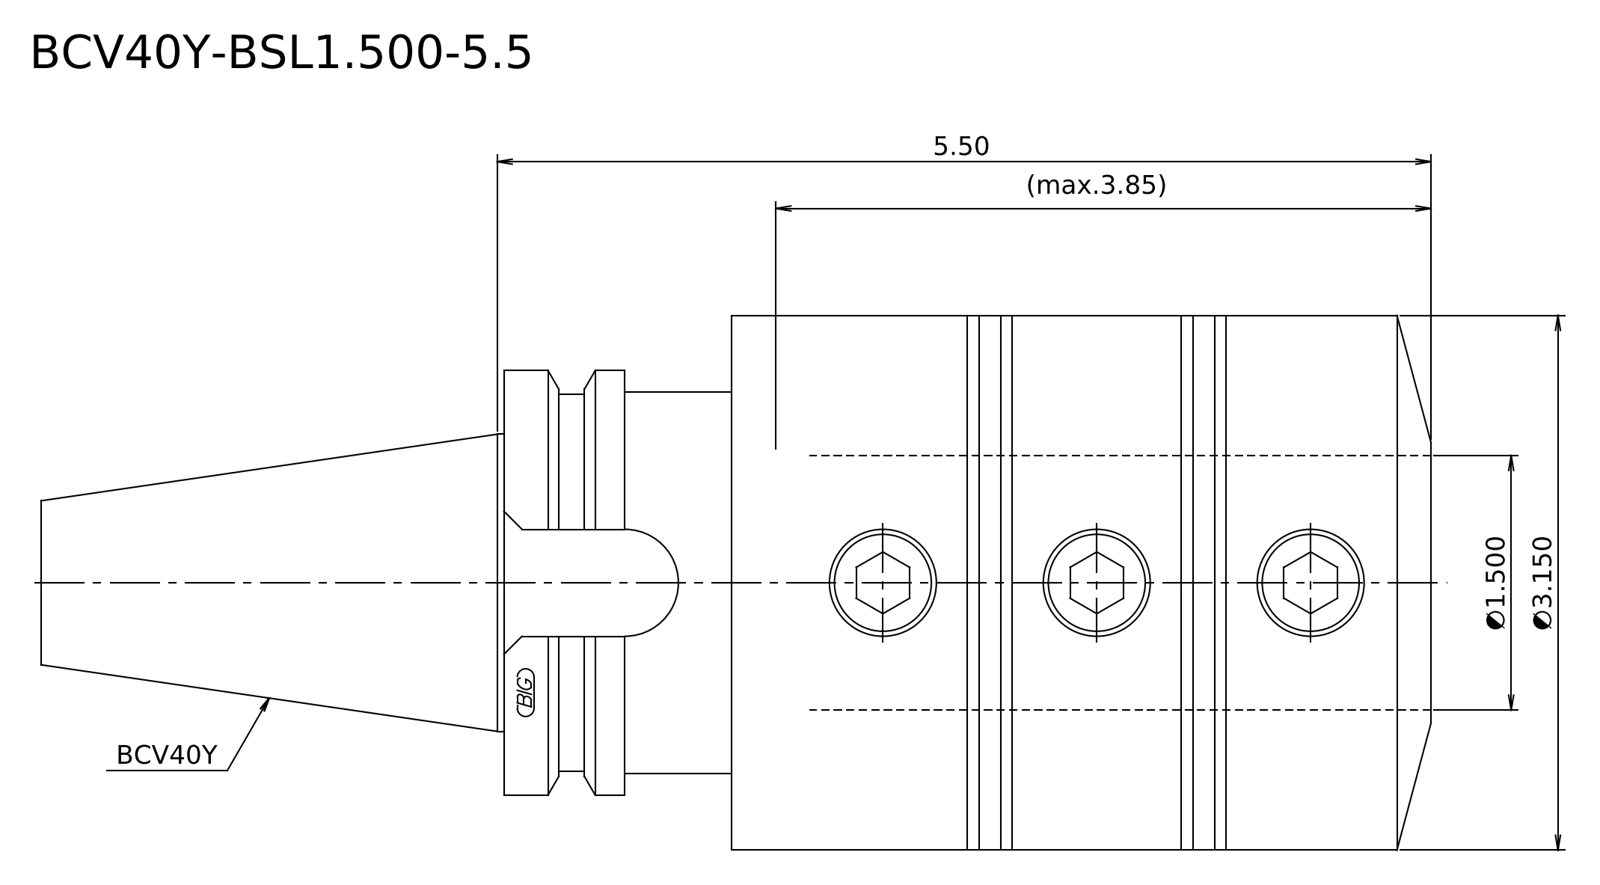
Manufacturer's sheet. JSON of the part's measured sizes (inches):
{"step_written_by": "Kubotek KeyCreator 2011 V10.0.2 (22737) (automotive_design)", "units": "inches", "bodies": {"solids": 1, "faces": 17, "planar": 7, "cylindrical": 6, "other": 4}, "overall_size": [8.187, 3.15, 3.15], "volume_in3": 41.35, "surface_area_in2": 77.84, "round_bosses_or_shafts": [[3.15, 1], [2.5, 1], [2.244, 1], [2.219, 1], [1.75, 1]], "face_to_face_distances": [1.339, 4.122, 5.461, 4.75, 0.628, 0.711, 8.187, 4.065, 3.437, 2.726]}
